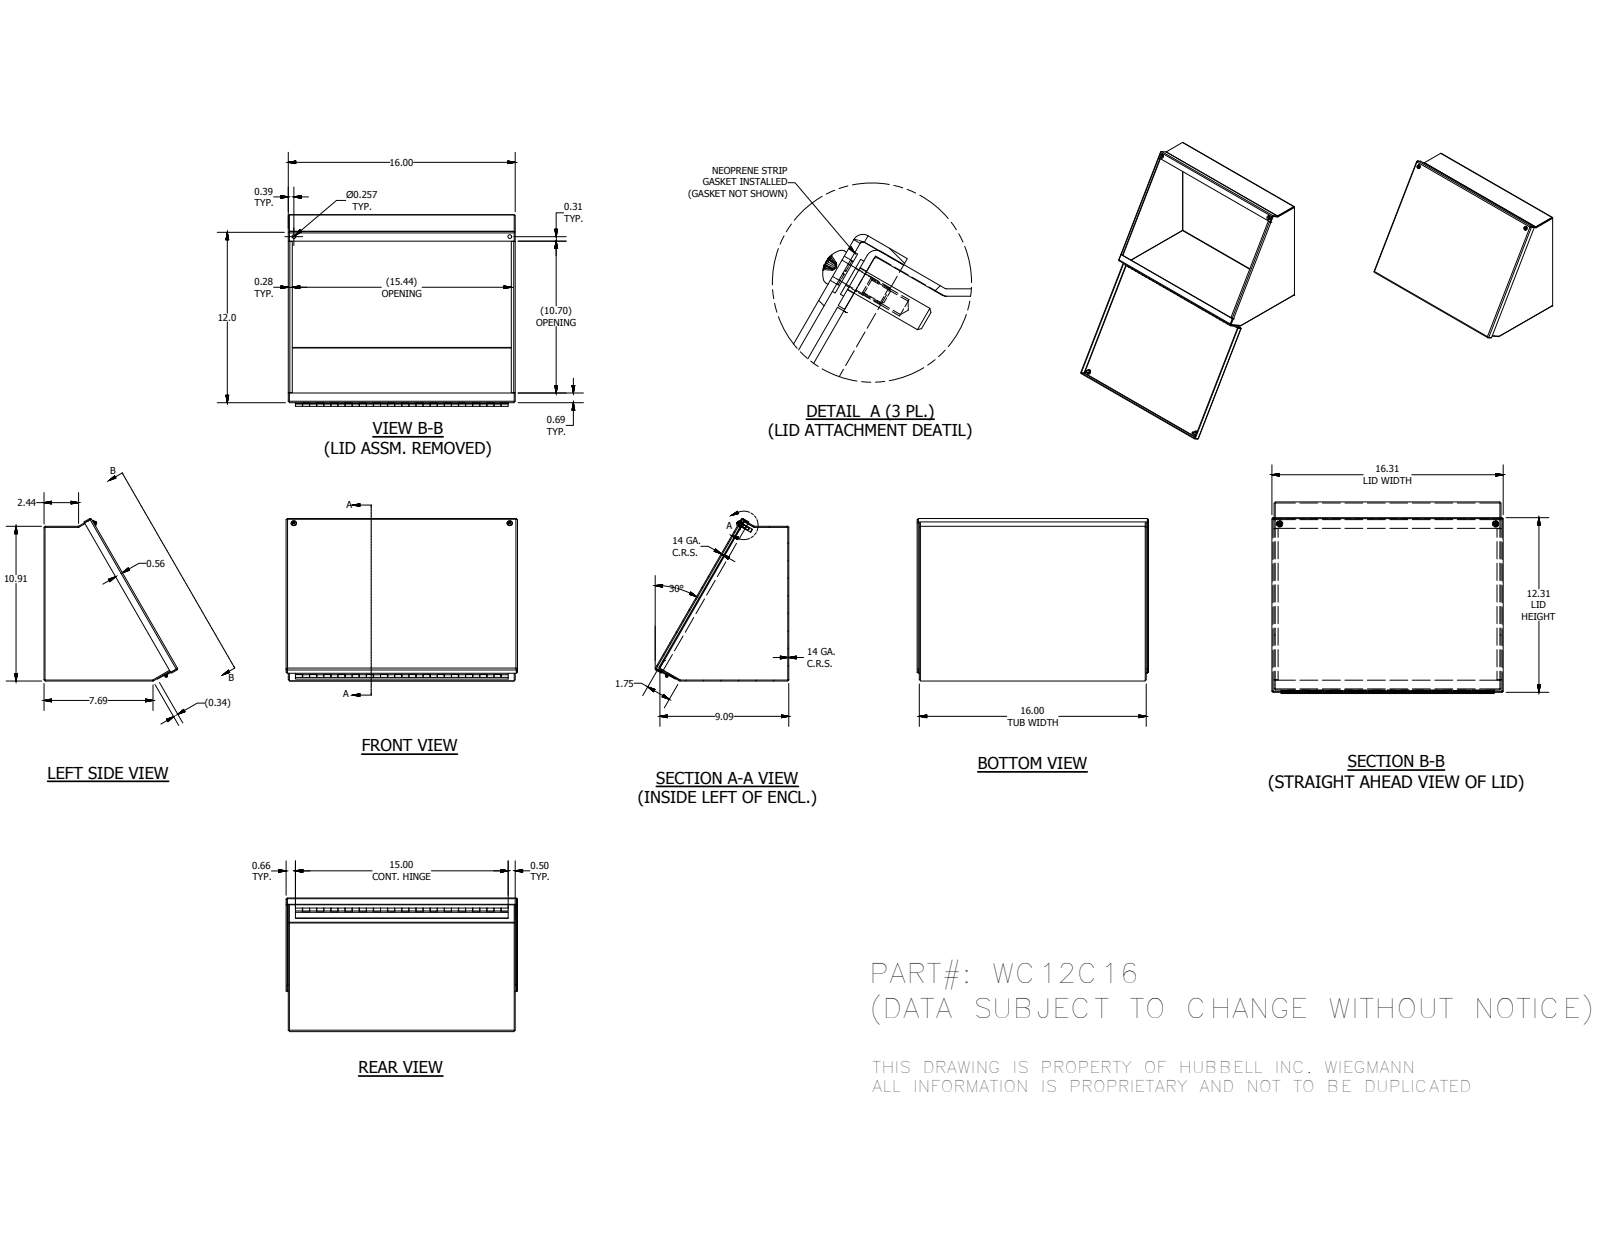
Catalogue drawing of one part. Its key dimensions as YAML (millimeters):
part_name: "WC12C16BTB; WC12C16LID; WC12CLS; WC12CRS (+6 more)"
step_written_by: "Autodesk Inventor 2014 (AP242_MANAGED_MODEL_BASED_3D_ENGINEERING_MIM_LF)"
units: millimeters
bodies: {solids: 12, faces: 368, planar: 233, cylindrical: 83, other: 52}
overall_size: [414.34, 290.93, 239.28]
volume: 931427
surface_area: 1011000
round_holes:
  - {diameter: 3.96, count: 2}
  - {diameter: 4.98, count: 2}
  - {diameter: 6.53, count: 2}
  - {diameter: 7.06, count: 2}
  - {diameter: 7.14, count: 2}
  - {diameter: 2.96, count: 1}
round_bosses_or_shafts:
  - {diameter: 11.51, count: 2}
  - {diameter: 10.31, count: 2}
  - {diameter: 9.47, count: 2}
  - {diameter: 6.3, count: 2}
  - {diameter: 4.83, count: 2}
  - {diameter: 5.08, count: 1}
  - {diameter: 2.54, count: 1}
partial_cylinders:
  - {radius: 0.79, count: 12}
  - {radius: 2.67, count: 12}
  - {radius: 2.27, count: 2}
face_to_face_distances: [1.88, 404.52, 275.14, 402.64, 406.4, 273.26, 277.02, 304.8, 3.97, 408.49]
hole_center_spacings: [386.74]
